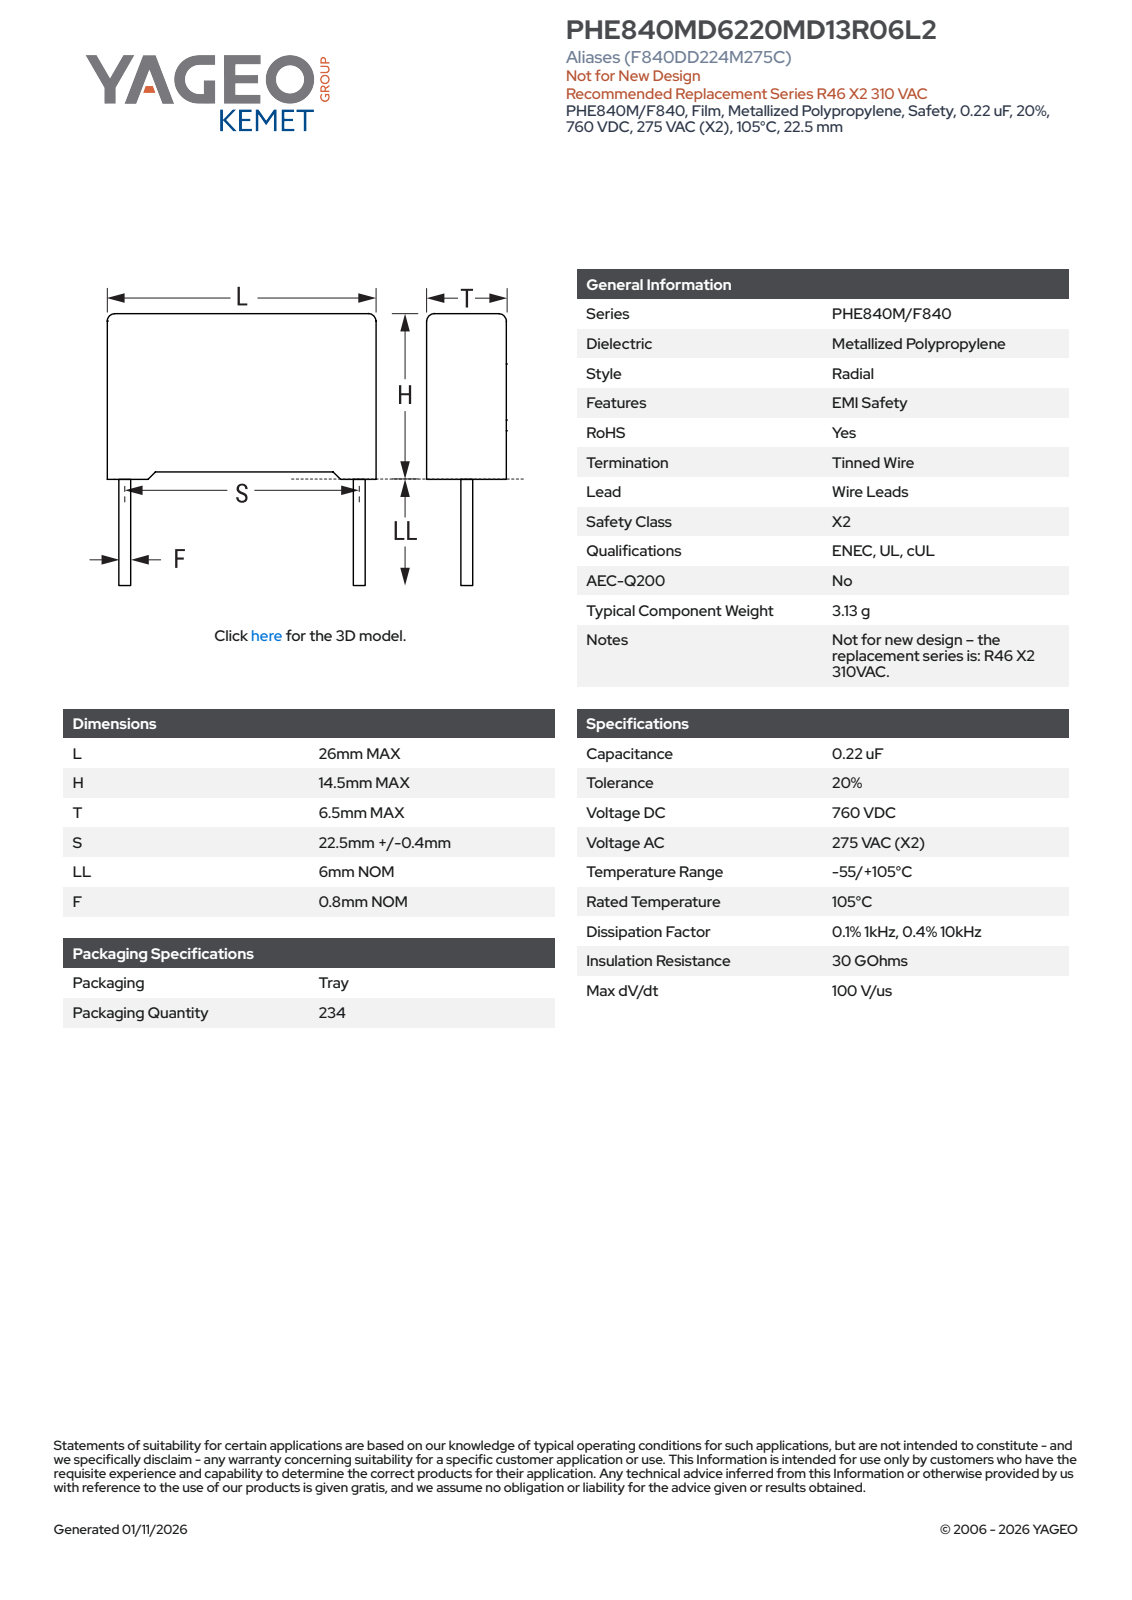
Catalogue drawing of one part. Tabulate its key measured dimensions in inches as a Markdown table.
| quantity | value |
| --- | --- |
| part name | CFR_RB2_26X14.5X6.5_L26H14.5T6.5S22.5LL6F0.8 |
| STEP written by | SolidWorks 2021 (AUTOMOTIVE_DESIGN) |
| units | inches |
| bodies | 4 solids, 85 faces (77 planar, 8 cylindrical, 0 other) |
| overall size | 1.024 × 0.807 × 0.256 |
| volume | 0.143 in³ |
| surface area | 2.105 in² |
| round bosses / shafts (diameter × count) | 0.031 × 2 |
| partial cylindrical surfaces (radius × count) | 0.02 × 4 |
| main face-to-face distances | 0.256, 0.541, 1.024, 0.551, 0.034, 0.02, 0.03, 0.571, 0.222, 0.187 |
